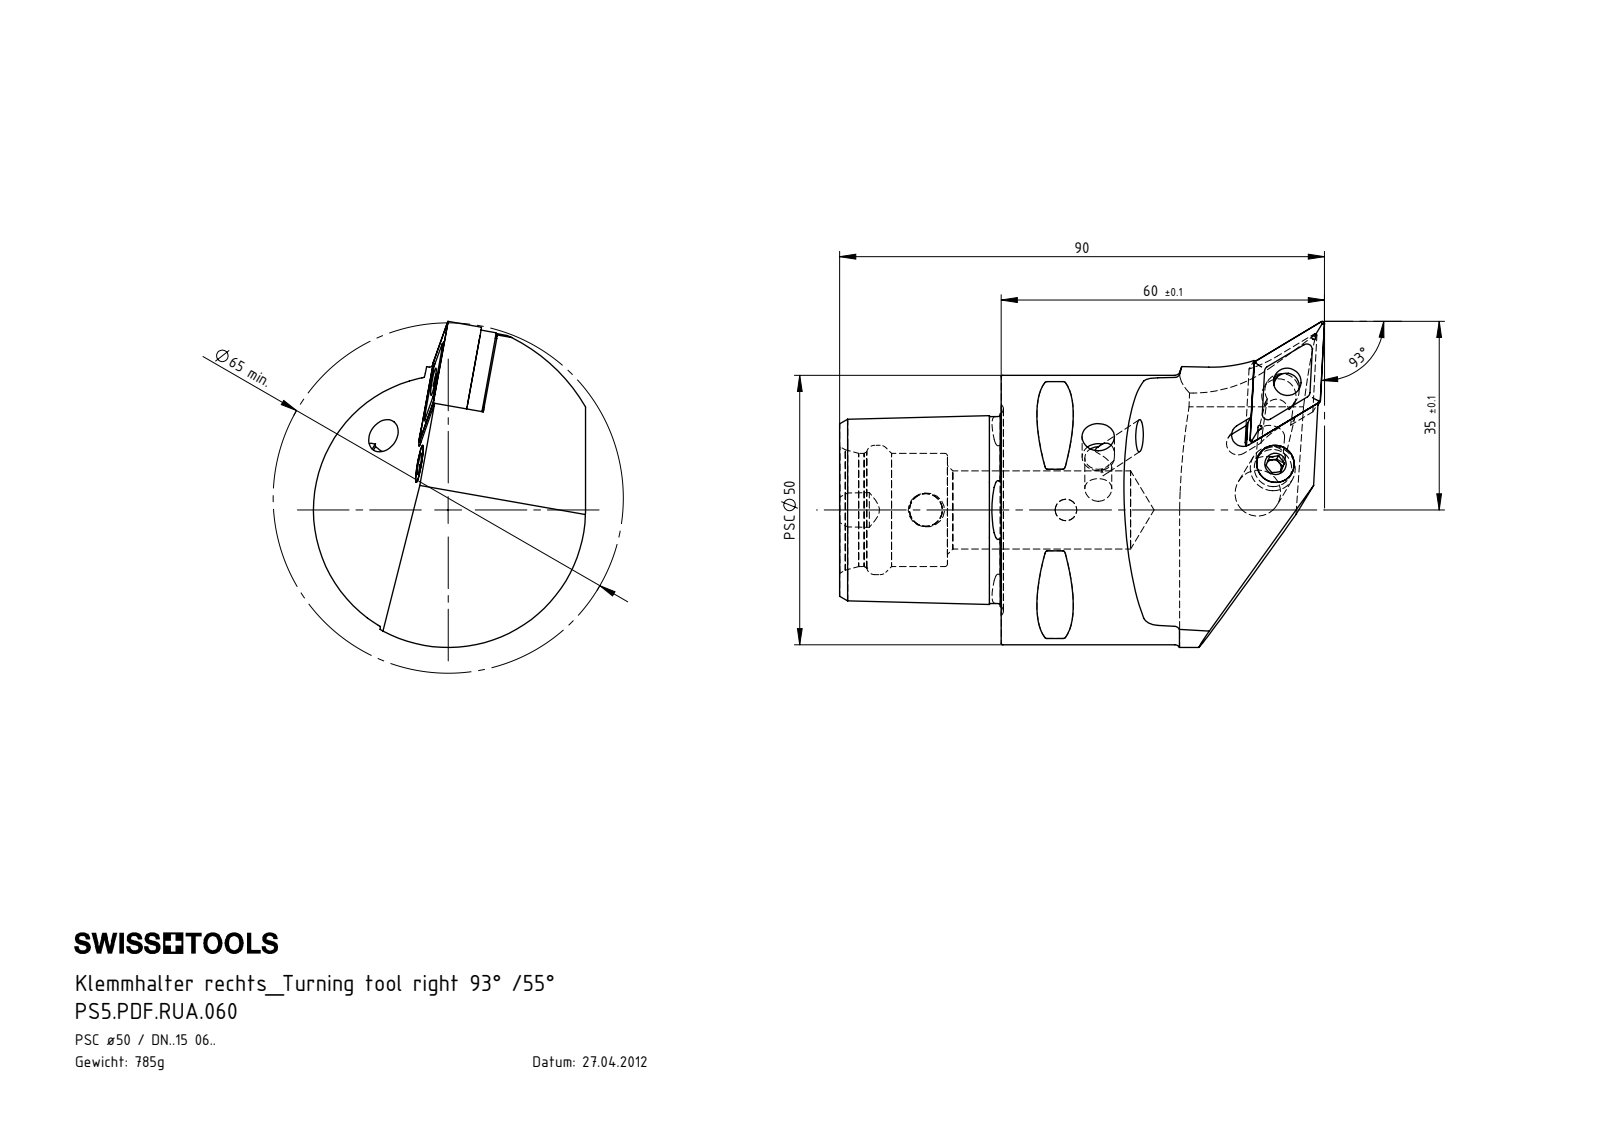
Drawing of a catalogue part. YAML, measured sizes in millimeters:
part_name: "WDF-ER2.101.003_A; WCD-ER4.101.017_A; WCD-ER1.101.000; DNMG150604 (+4 more)"
step_written_by: "SolidWorks 2017 (AUTOMOTIVE_DESIGN)"
units: millimeters
bodies: {solids: 8, faces: 256, planar: 92, cylindrical: 54, other: 110}
overall_size: [90, 60.5, 50.5]
volume: 100531
surface_area: 22703
round_holes:
  - {diameter: 5, count: 3}
  - {diameter: 4, count: 1}
  - {diameter: 5.16, count: 1}
  - {diameter: 6, count: 1}
  - {diameter: 6.1, count: 1}
  - {diameter: 6.4, count: 1}
  - {diameter: 7, count: 1}
  - {diameter: 8.4, count: 1}
  - {diameter: 14.5, count: 1}
  - {diameter: 21, count: 1}
  - {diameter: 24, count: 1}
round_bosses_or_shafts:
  - {diameter: 50, count: 1}
  - {diameter: 8, count: 1}
  - {diameter: 7.9, count: 1}
  - {diameter: 6.4, count: 1}
  - {diameter: 6, count: 1}
  - {diameter: 4.7, count: 1}
  - {diameter: 3.55, count: 1}
partial_cylinders:
  - {radius: 0.5, count: 8}
  - {radius: 0.4, count: 4}
  - {radius: 1, count: 4}
  - {radius: 2.5, count: 2}
  - {radius: 3.2, count: 2}
  - {radius: 25.5, count: 2}
  - {radius: 2.1, count: 1}
  - {radius: 2.35, count: 1}
face_to_face_distances: [30, 6.02, 3.18, 9.2, 12.7, 12.31, 19.18, 4.85, 44.4, 0.39]
hole_center_spacings: [15.6, 15.61, 26]
